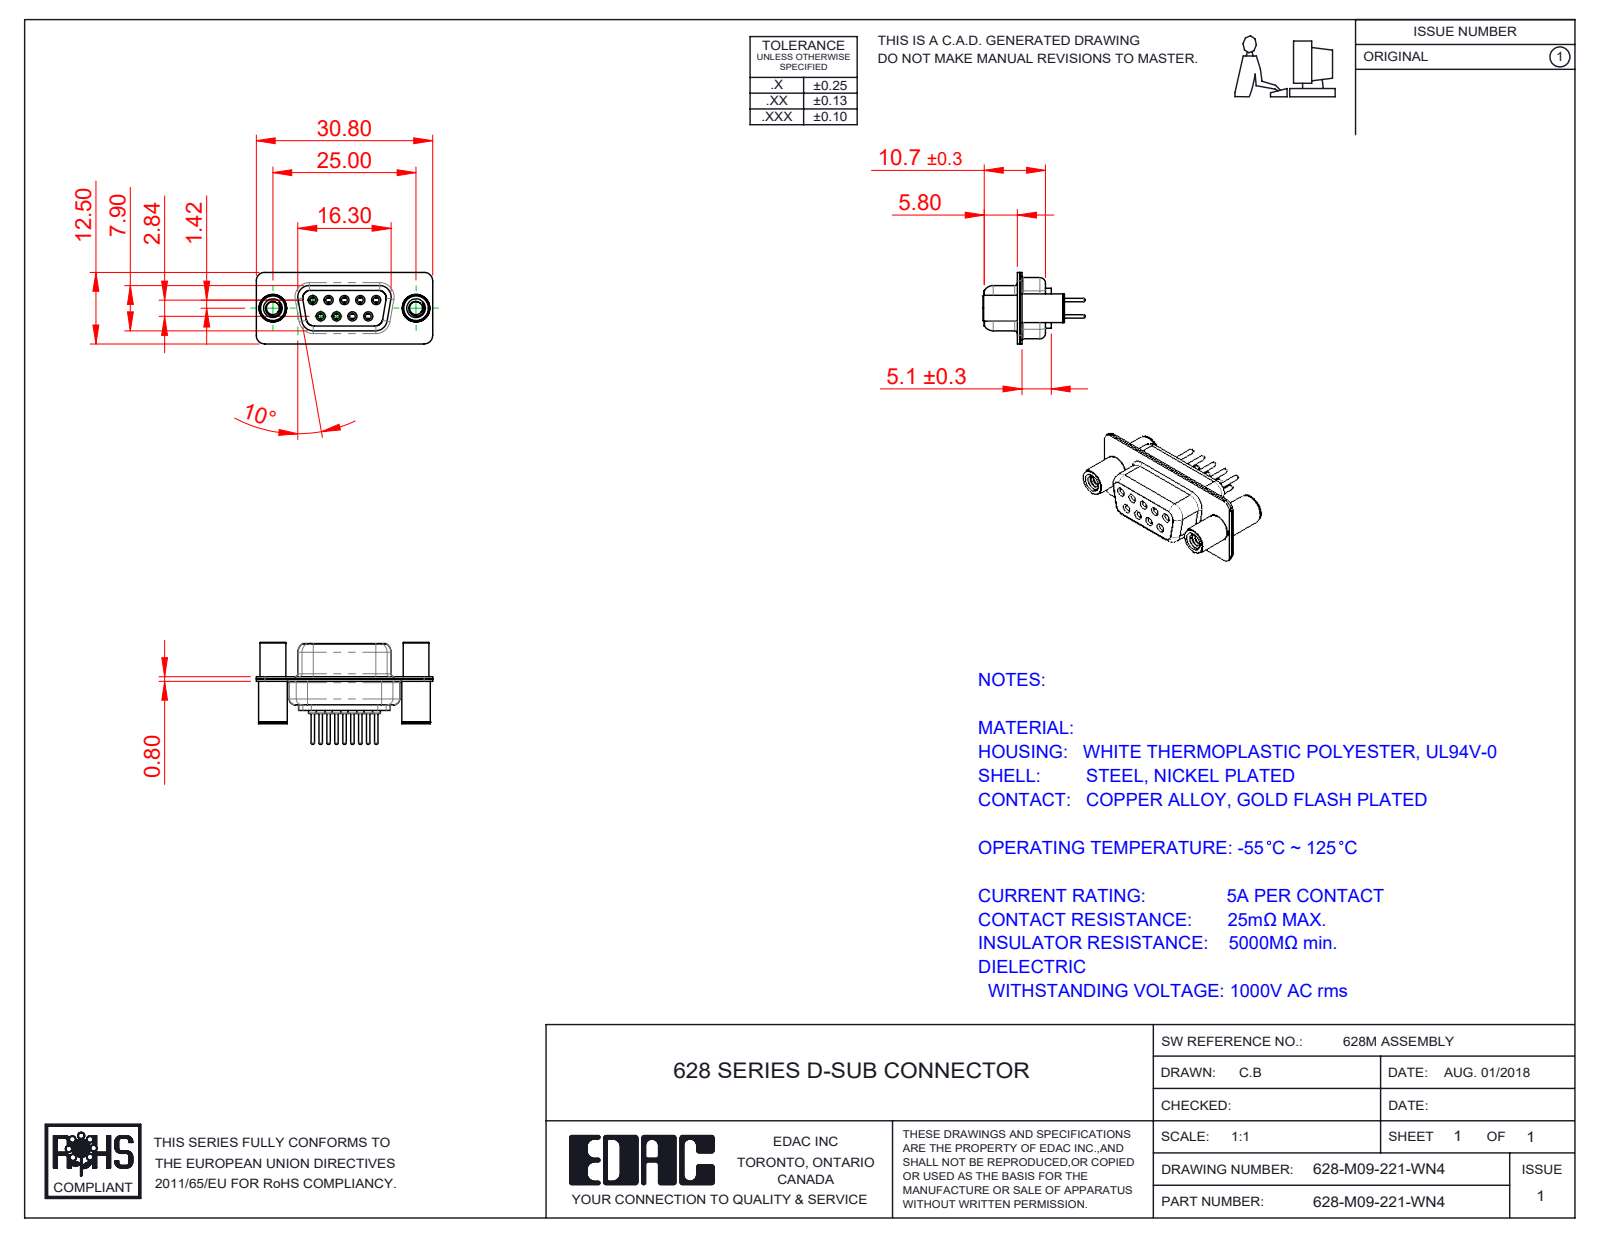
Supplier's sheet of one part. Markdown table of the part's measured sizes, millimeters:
| quantity | value |
| --- | --- |
| part name | 628M Contact Row 1_21; 628M 4-40 Threaded Standoff and Board Spacer; 628M Shell Rear_09 Contacts; 628-M09-221-WN4 (+3 more) |
| STEP written by | SolidWorks 2020 (CONFIG_CONTROL_DESIGN) |
| units | millimeters |
| bodies | 14 solids, 860 faces (208 planar, 360 cylindrical, 292 other) |
| overall size | 30.8 × 17.8 × 12.5 |
| volume | 1 989 mm³ |
| surface area | 4 952 mm² |
| round holes (diameter × count) | 1 × 9, 1.1 × 9, 1.7 × 9, 1.8 × 9, 2 × 9, 2.26 × 2, 3.26 × 2, 4 × 2, 4.8 × 2 |
| round bosses / shafts (diameter × count) | 2.2 × 9, 1.6 × 9, 1.5 × 9, 0.6 × 9, 5 × 2, 4.9 × 2, 4.5 × 2 |
| partial cylindrical surfaces (radius × count) | 1.5 × 16, 2 × 12, 1.35 × 8, 1.6 × 8, 0.25 × 4, 0.5 × 4, 0.6 × 4, 0.65 × 4 |
| main face-to-face distances | 0.4, 1.4, 0.45, 8.45, 0.8, 1.8, 8.9, 1, 6.2, 7.05 |
| hole center spacings | 3.16, 2.77, 5.54, 5.03, 5.04, 8.31, 7.1, 7.48 |
